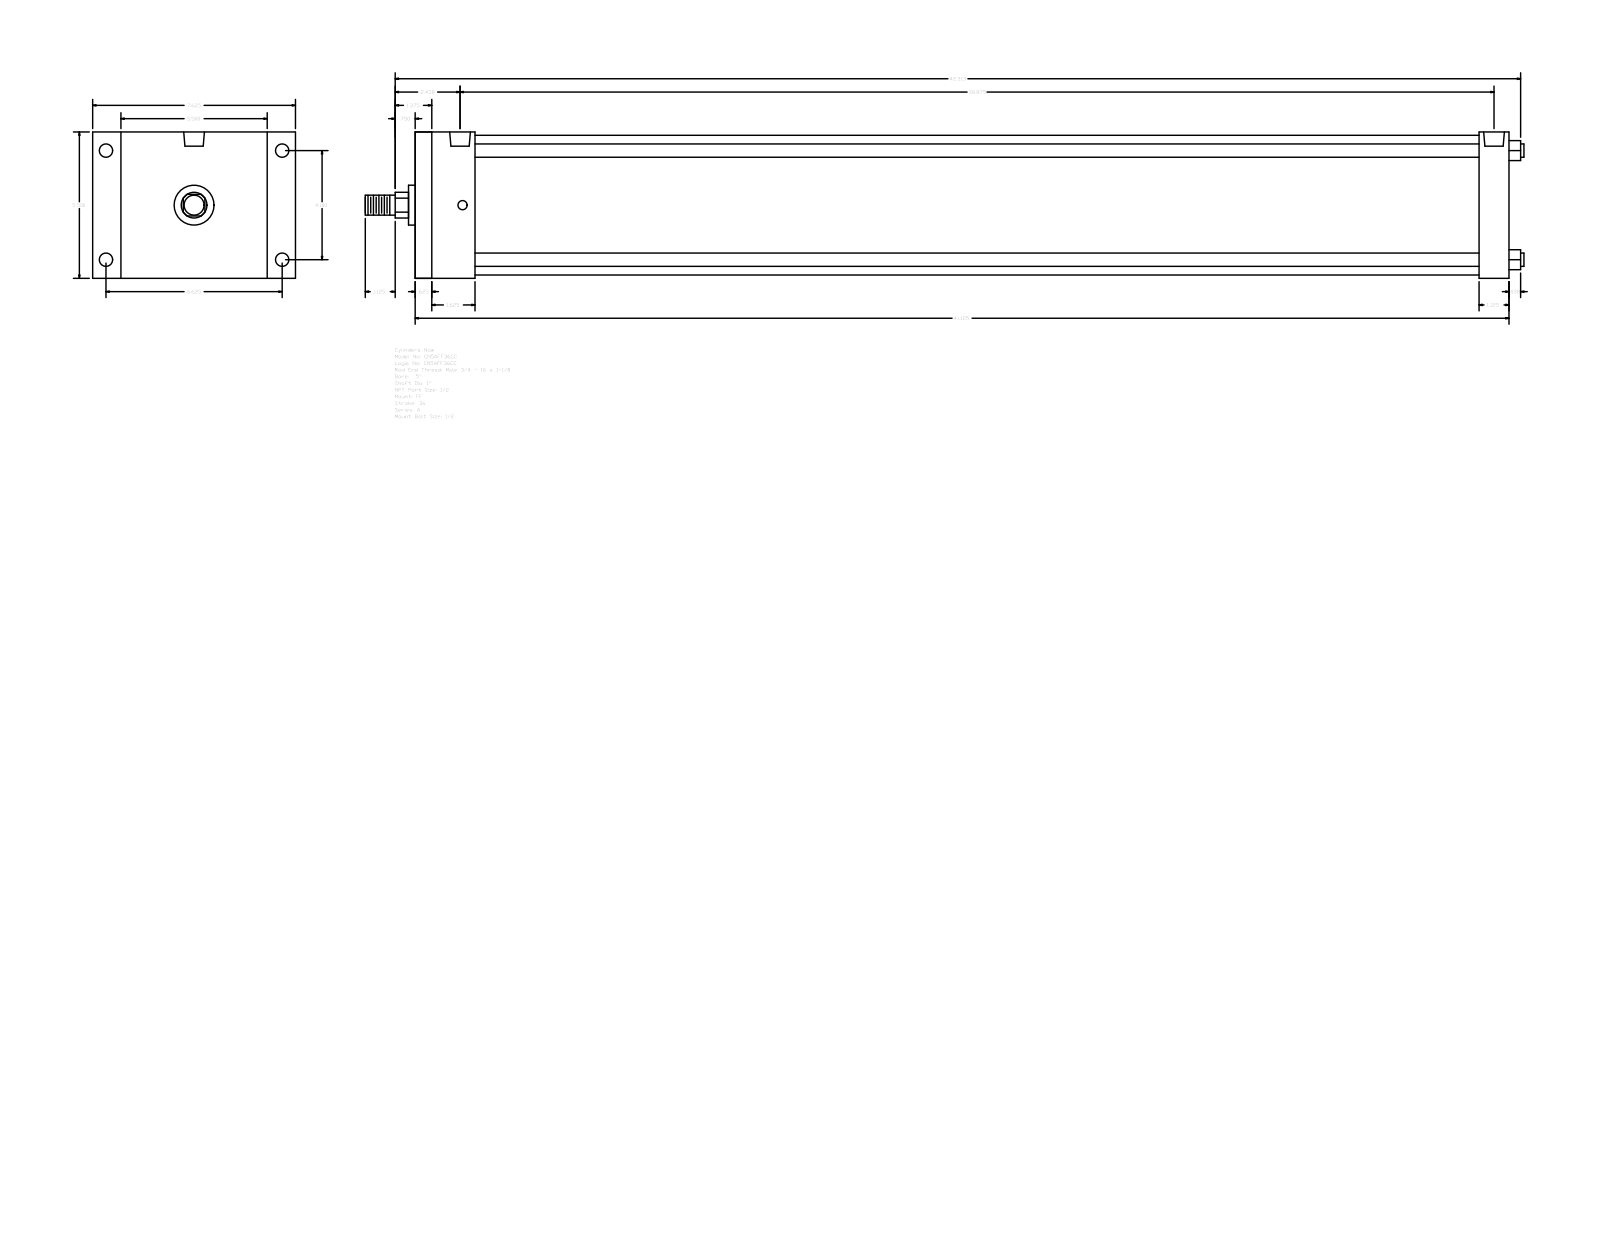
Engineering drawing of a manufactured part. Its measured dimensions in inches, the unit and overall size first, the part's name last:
Units: inches
Overall size (bounding box): 43.563 × 7.625 × 5.5
Round holes (diameter × count): ⌀0.344 ×4, ⌀0.5 ×4, ⌀0.778 ×2
Round bosses / shafts (diameter × count): ⌀0.5 ×4, ⌀5.25 ×1, ⌀1.5 ×1, ⌀1 ×1, ⌀0.75 ×1
Partial cylindrical surfaces — rounded edges, fillets, slot ends (radius × count): R0.484 ×1
Main face-to-face distances: 5.5, 41.125, 0.625, 40.5, 1.125, 40, 39.375, 2.25, 1.625, 37.75
Hole centre spacings: 0.094, 4.1, 6.625, 7.791, 38.687, 38.781, 38.875
Bodies: 0 solids, 92 faces (64 planar, 28 cylindrical, 0 other)
Part name (STEP PRODUCT): A_FF__0500_1
STEP written by: GSSL Pune (CONFIG_CONTROL_DESIGN)
